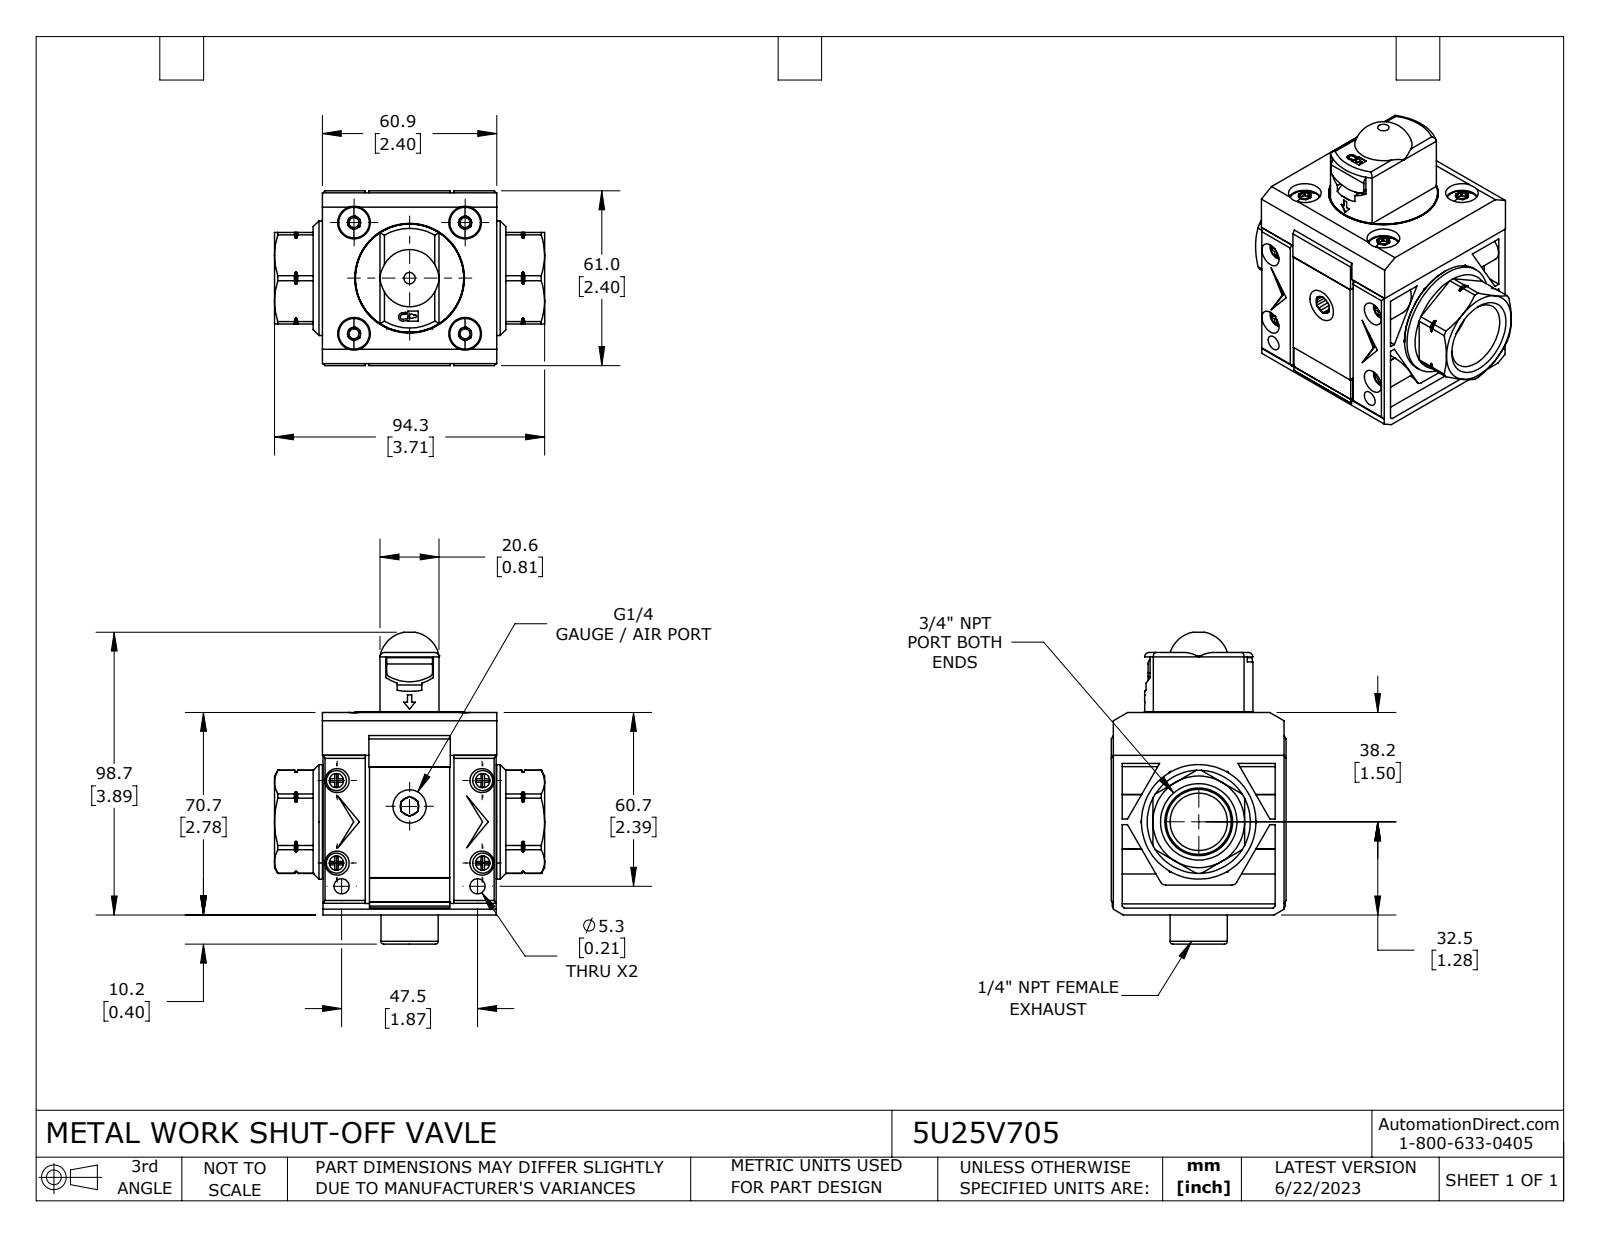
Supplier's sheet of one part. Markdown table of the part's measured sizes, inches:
| quantity | value |
| --- | --- |
| part name | 5U25V705 |
| STEP written by | SolidWorks 2021 (CONFIG_CONTROL_DESIGN) |
| units | inches |
| bodies | 13 solids, 954 faces (460 planar, 280 cylindrical, 214 other) |
| overall size | 4.288 × 3.713 × 2.402 |
| volume | 14.89 in³ |
| surface area | 122.1 in² |
| round holes (diameter × count) | 0.128 × 4, 0.165 × 4, 0.331 × 4, 0.449 × 4, 0.209 × 2, 0.451 × 1, 0.457 × 1, 0.787 × 1, 1.248 × 1, 1.508 × 1 |
| round bosses / shafts (diameter × count) | 0.276 × 4, 0.189 × 4, 0.15 × 4, 1.575 × 1, 1.496 × 1, 1.378 × 1, 1.035 × 1, 0.925 × 1 |
| partial cylindrical surfaces (radius × count) | 0.011 × 24, 0.059 × 4, 0.069 × 4, 0.191 × 4, 0.079 × 2, 0.242 × 2, 0.591 × 2, 0.018 × 1 |
| main face-to-face distances | 0.094, 2.39, 2.193, 2.098, 2.402, 0.299, 0.028, 1.799, 2.382, 0.394 |
| hole center spacings | 1.08, 1.528, 0.325, 1.057, 1.134, 1.265, 1.443, 1.454 |
